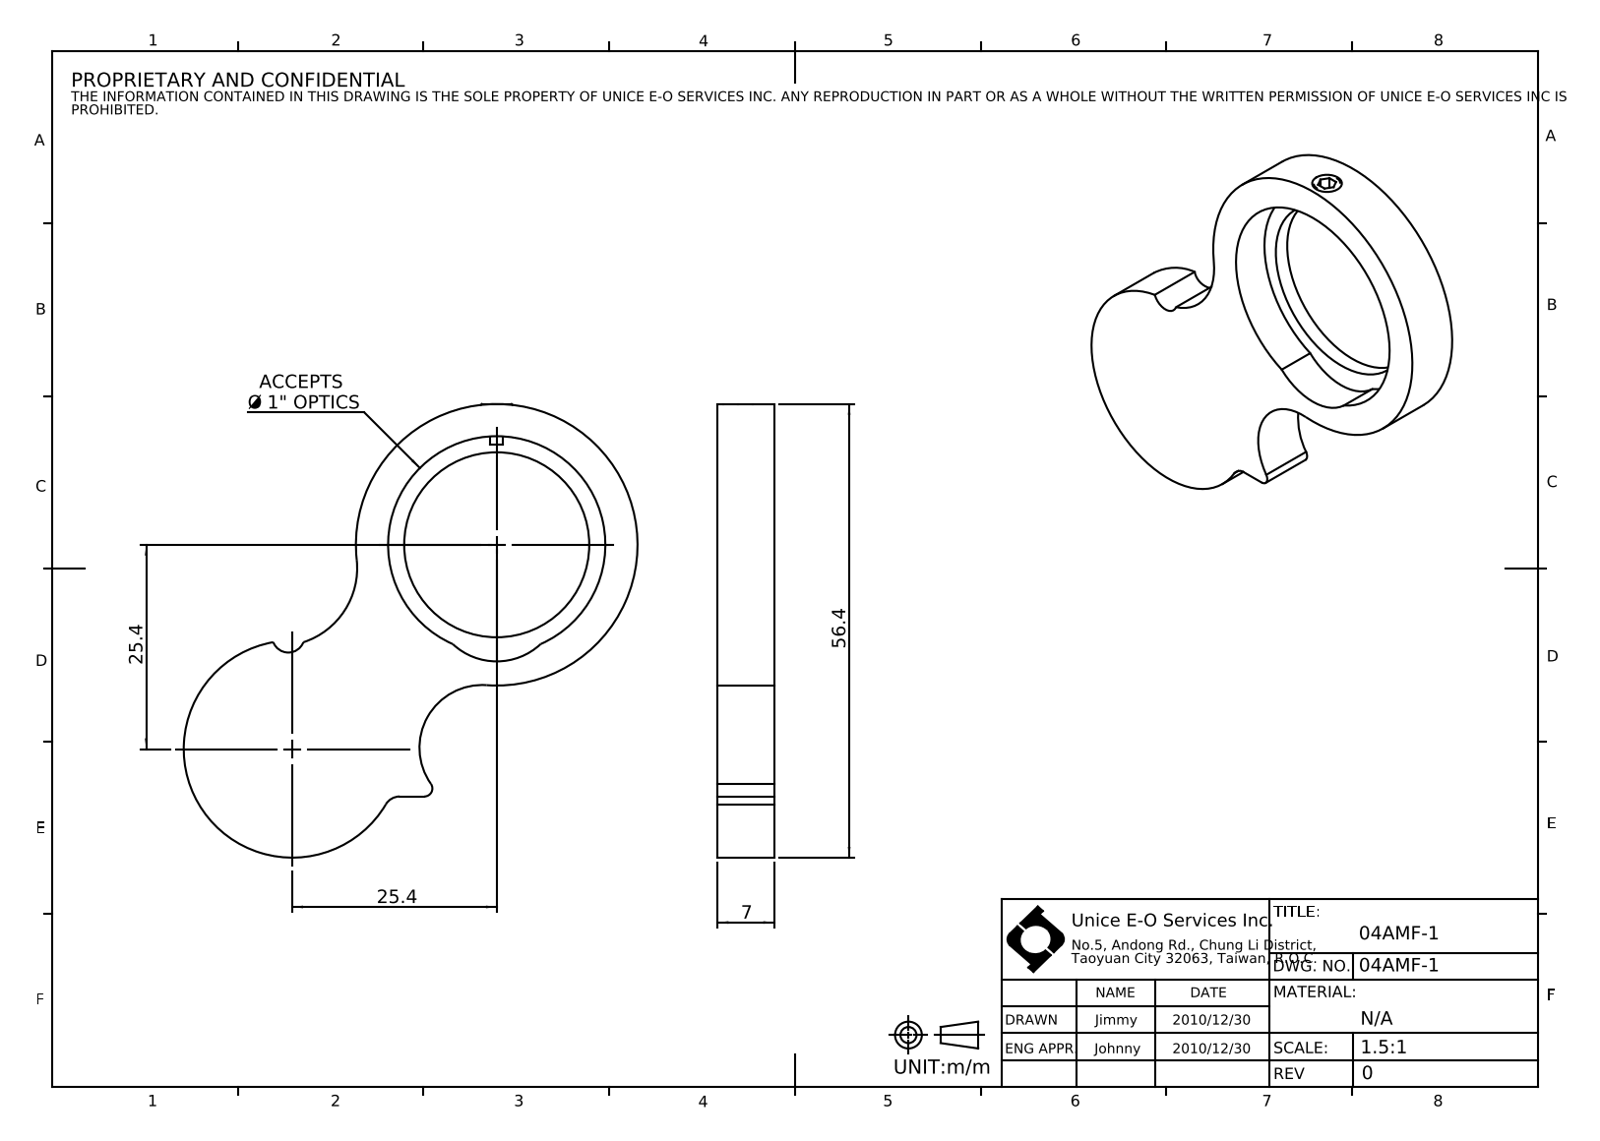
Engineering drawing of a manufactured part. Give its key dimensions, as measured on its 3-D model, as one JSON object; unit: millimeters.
{"part_name": "04AMF-1", "step_written_by": "SolidWorks 2016 (CONFIG_CONTROL_DESIGN)", "units": "millimeters", "bodies": {"solids": 3, "faces": 46, "planar": 15, "cylindrical": 25, "other": 6}, "overall_size": [56.4, 56.4, 7], "volume_mm3": 7960, "surface_area_mm2": 4489, "round_holes": [[1.5, 1], [3.3, 1], [23, 1], [27, 1]], "round_bosses_or_shafts": [[4, 1], [1.6, 1]], "partial_cylinders_radius": [[2, 2], [1, 1], [7.8, 1], [8, 1], [9.7, 1], [13.5, 1], [17.5, 1]], "face_to_face_distances": [7, 2, 5, 1.5, 48.8, 3.5, 44.8, 4, 2.5, 46.3]}
